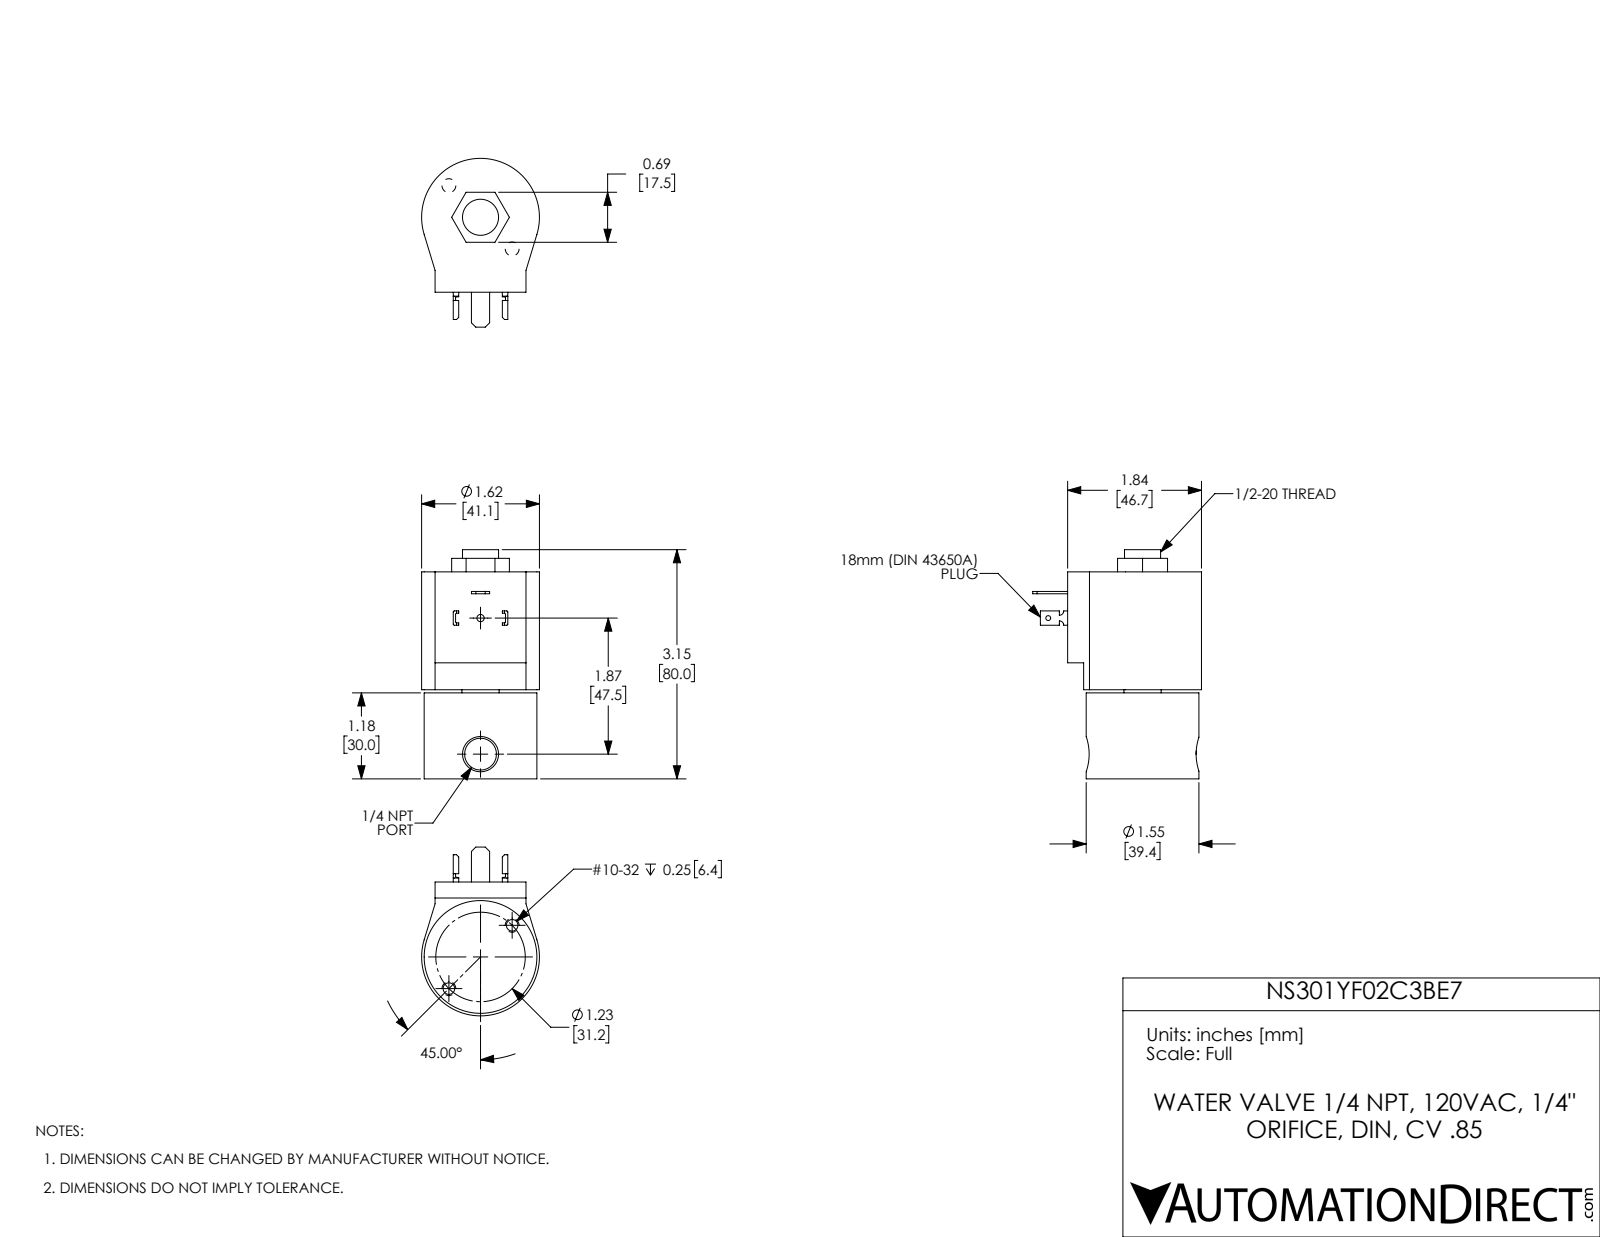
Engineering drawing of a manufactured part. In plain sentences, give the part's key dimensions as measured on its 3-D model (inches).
The part is named "NS301YF02C3BE7". Its 3-D file was written by "SolidWorks 2017 (AUTOMOTIVE_DESIGN)". It is 6 solids with 130 faces: 73 planar, 49 cylindrical and 8 other. Overall it measures 3.15 by 2.32 by 1.62 inches. Its volume is 6.027 cubic inches and its surface area 33.08 square inches. Round holes: 2 of diameter 0.159, 1 of diameter 0.067, 1 of diameter 0.1, 1 of diameter 0.437, 1 of diameter 0.496, 1 of diameter 0.512, 1 of diameter 1.155. Round bosses or shafts: 1 of diameter 1.55. Partial cylindrical surfaces (rounded edges, fillets, slot ends): 8 of radius 0.015, 2 of radius 0.06, 1 of radius 0.81. The main face-to-face distances are 2.845, 1.182, 1.663, 1.225, 0.043, 1.62, 1.287, 0.106, 0.062, 1.558. The hole center spacings are 0.615, 1.23, 1.87.
